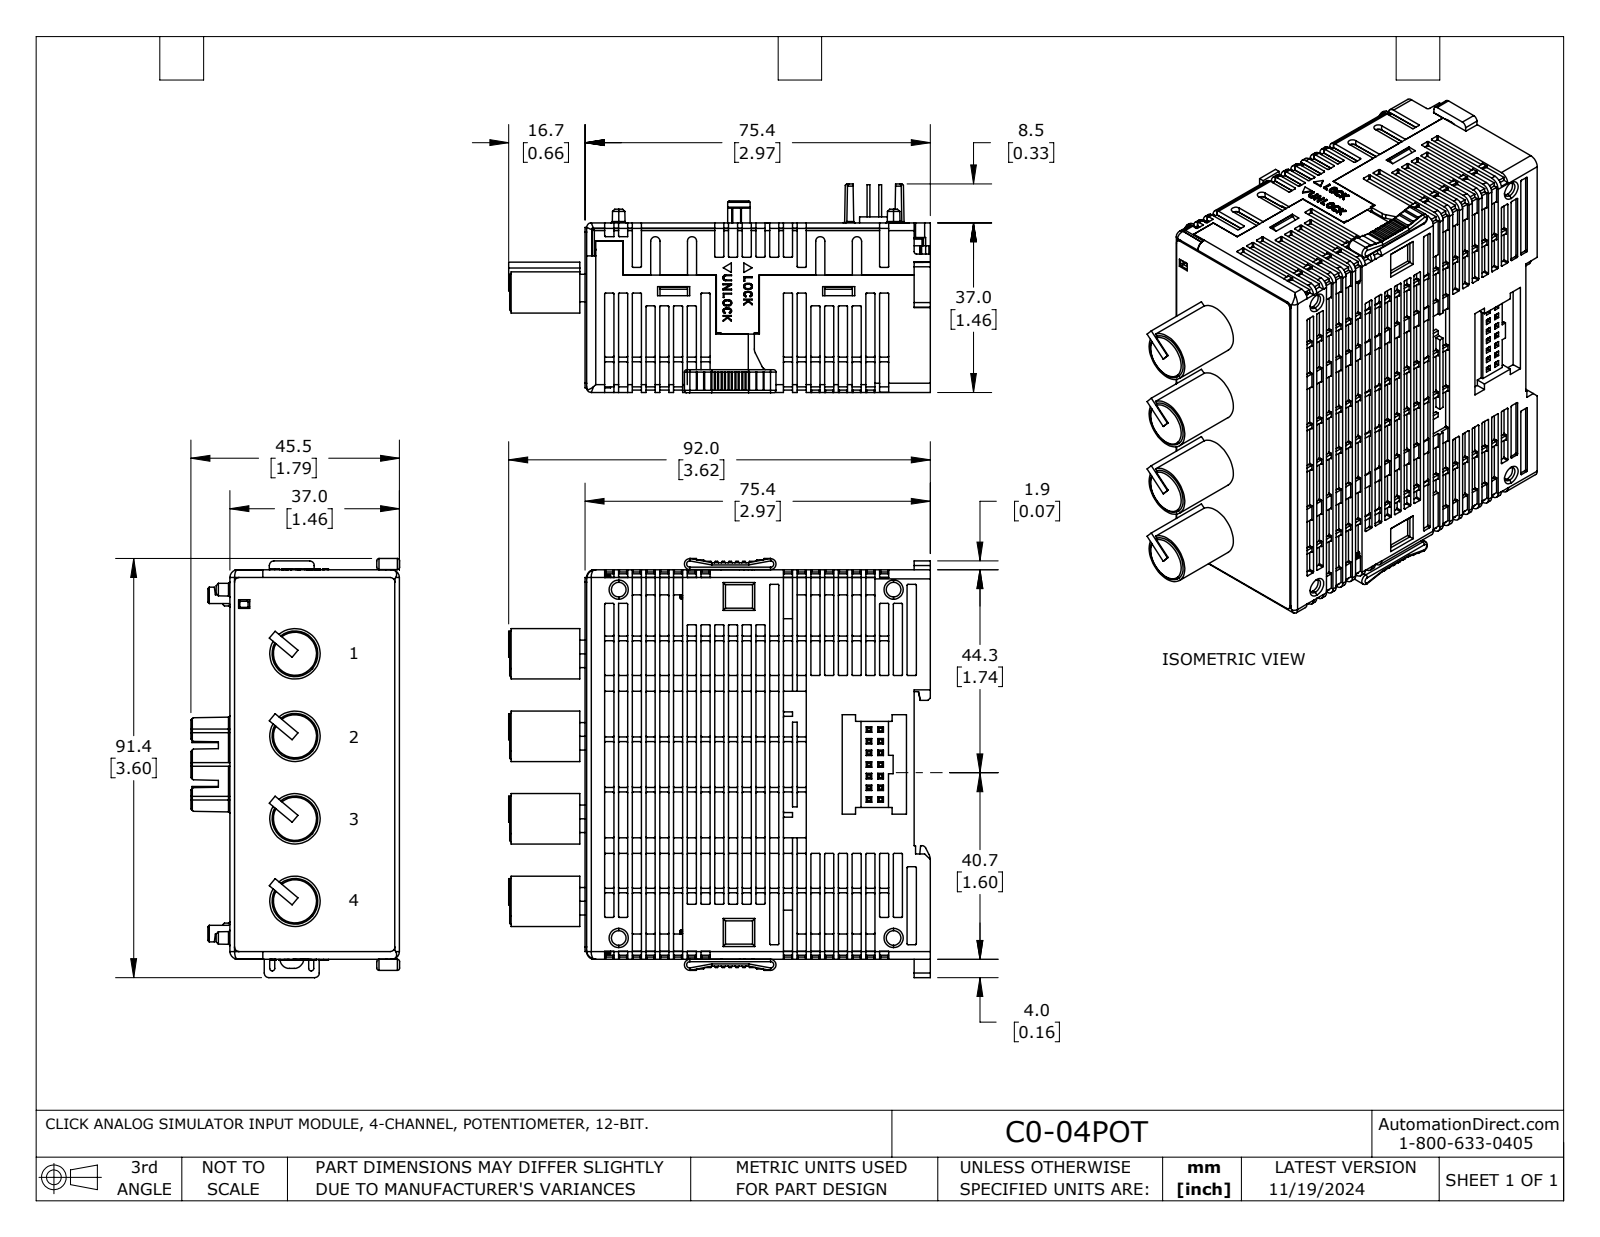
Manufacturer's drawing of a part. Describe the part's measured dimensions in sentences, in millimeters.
The part is named "C0-04POT". Its 3-D file was written by "SolidWorks 2024 (AUTOMOTIVE_DESIGN)". It is 2 solids with 4219 faces: 3087 planar, 1045 cylindrical and 87 other. Overall it measures 92 by 91.4 by 45.5 millimeters. Its volume is 230 200 cubic millimeters and its surface area 44 030 square millimeters. Round holes: 4 of diameter 3.2, 4 of diameter 7, 2 of diameter 2. Round bosses or shafts: 4 of diameter 11, 4 of diameter 6, 1 of diameter 1.9. Partial cylindrical surfaces (rounded edges, fillets, slot ends): 651 of radius 0.2, 52 of radius 0.5, 36 of radius 1, 33 of radius 0.3, 13 of radius 0.1, 6 of radius 1.7, 5 of radius 2, 4 of radius 1.2. The main face-to-face distances are 1.2, 37, 71.9, 35.8, 70.6, 85, 0.5, 3, 0.7, 2. The hole center spacings are 18, 36, 60, 76, 96.8, 10.4, 11.3, 11.5.
